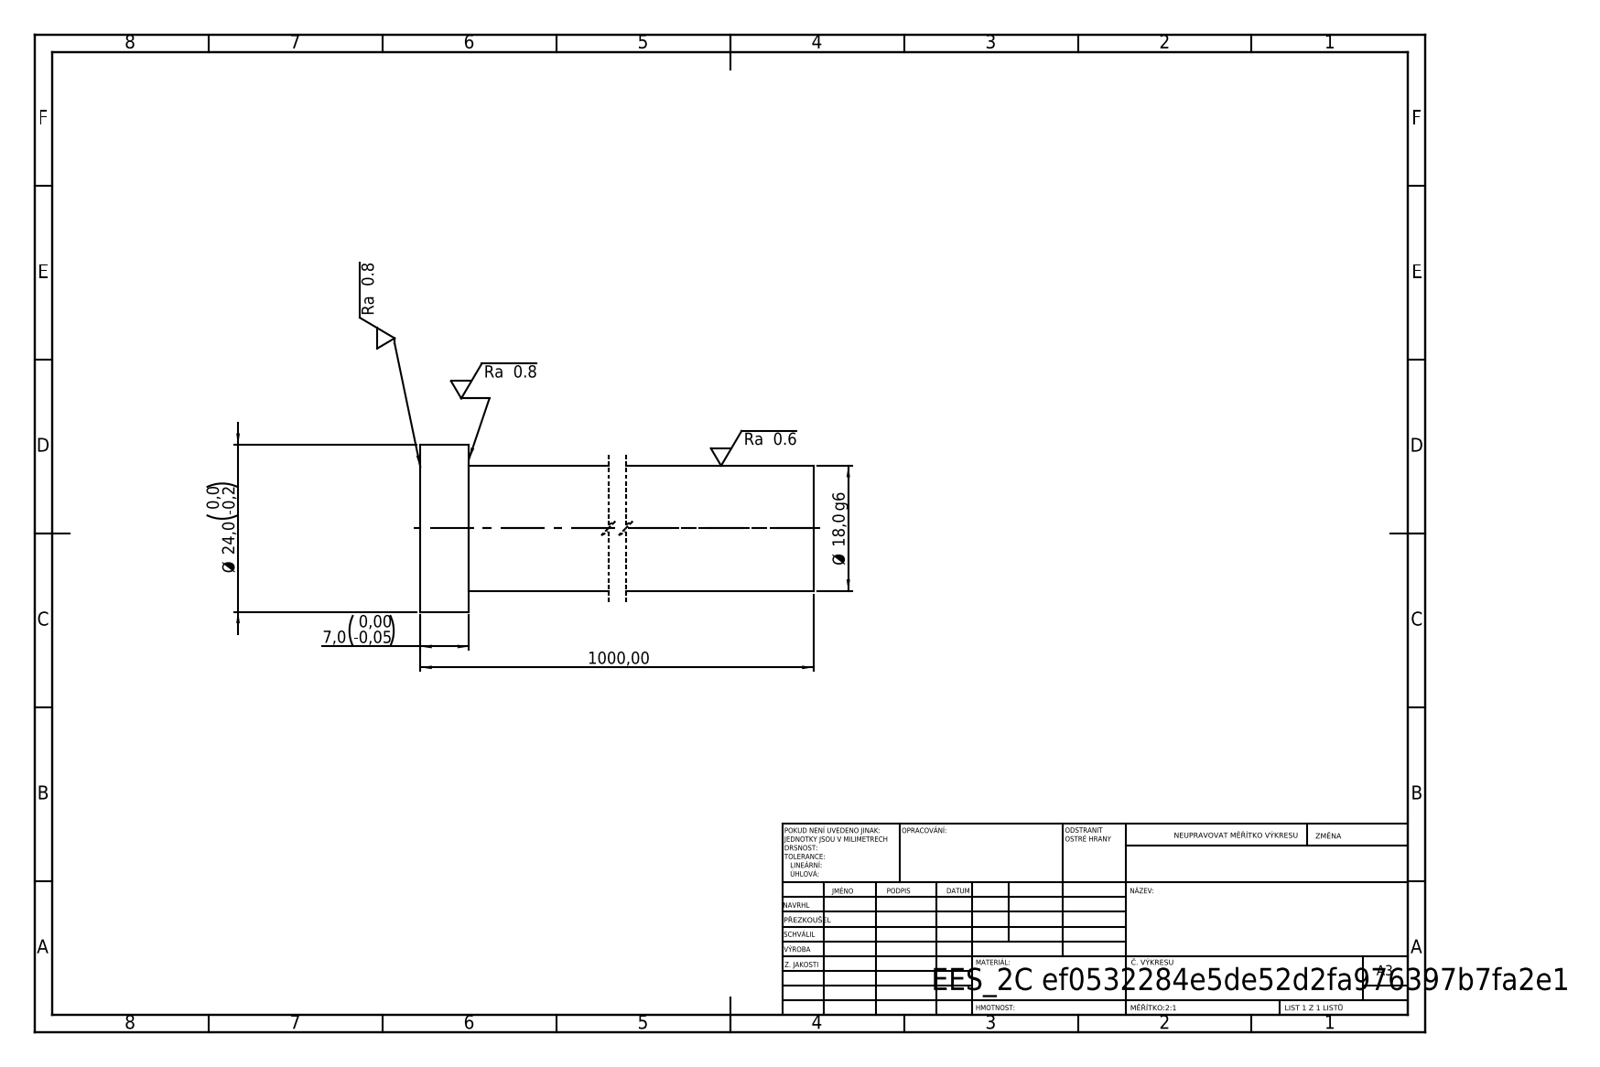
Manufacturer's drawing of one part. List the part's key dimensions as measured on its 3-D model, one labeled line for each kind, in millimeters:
STEP written by: SolidWorks 2019 (CONFIG_CONTROL_DESIGN)
Units: millimetres
Bodies: 1 solid, 7 faces (3 planar, 4 cylindrical, 0 other)
Overall size (bounding box): 1000 × 24 × 24
Volume: 255 854 mm³ · Surface area: 57 585 mm²
Round bosses / shafts (diameter × count): ⌀24 ×1, ⌀18 ×1
Main face-to-face distances: 1000, 7, 993
